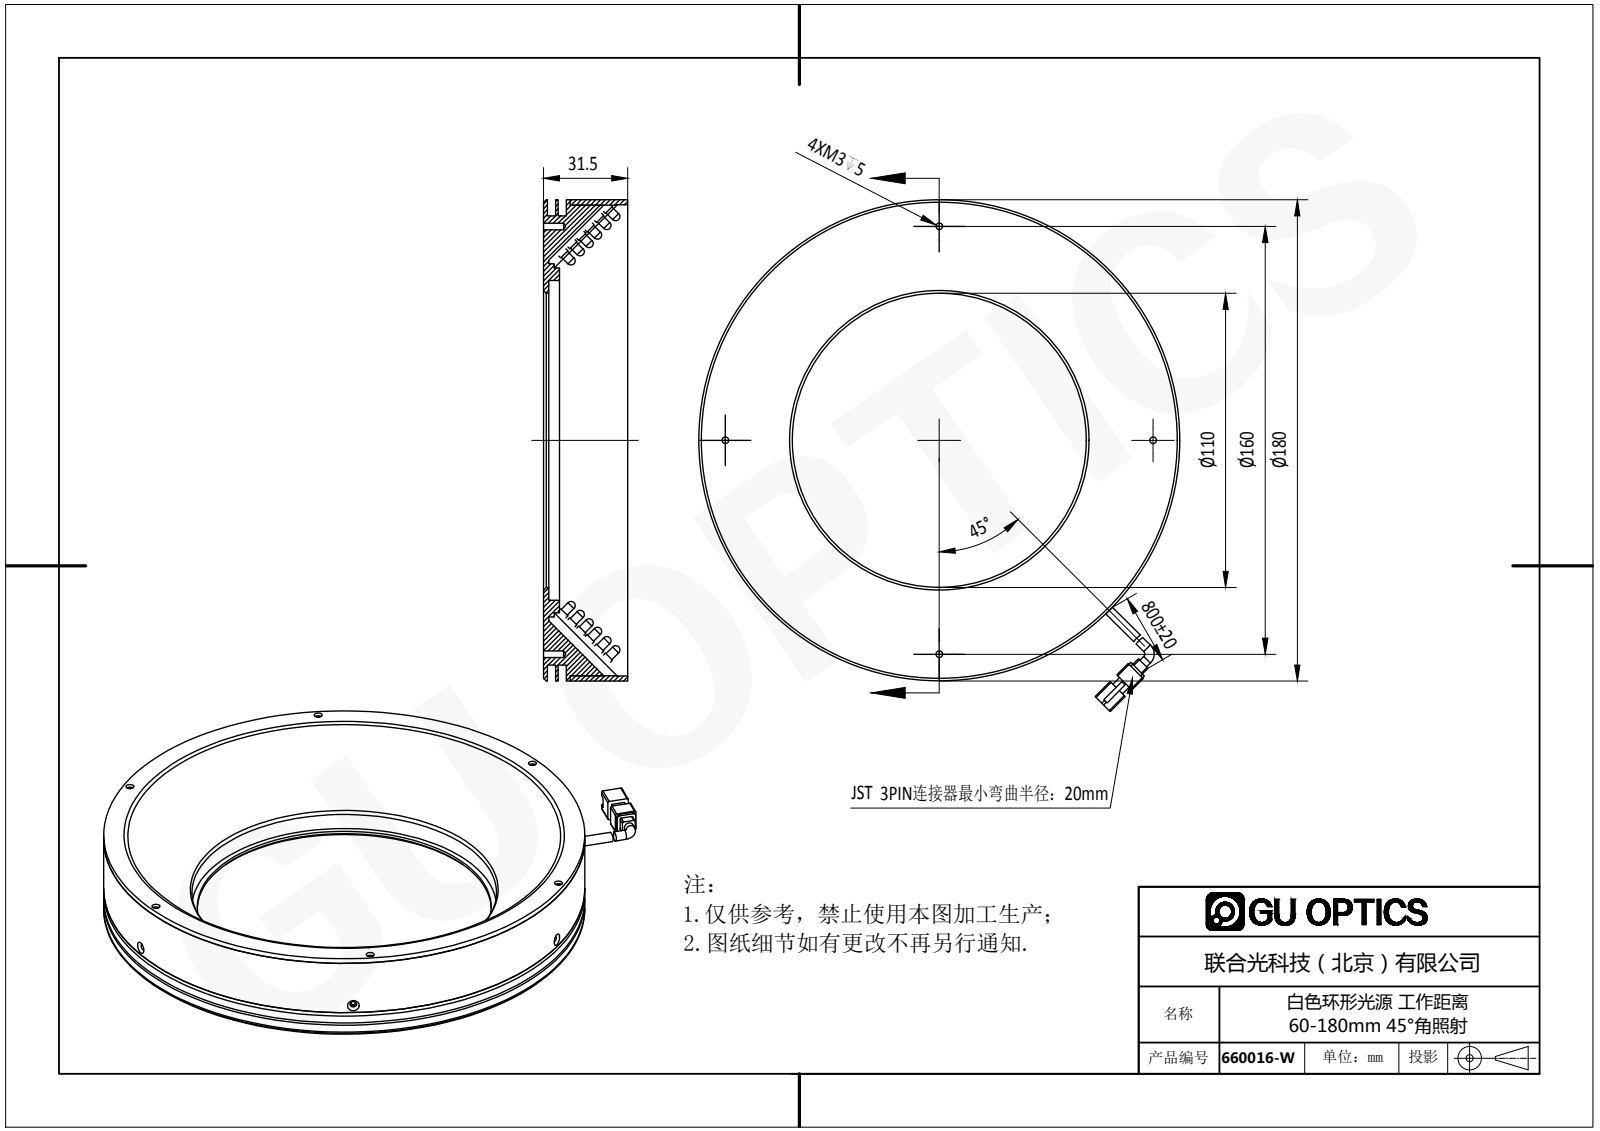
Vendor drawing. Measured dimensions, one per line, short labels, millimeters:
name: 660016-W
written by: SolidWorks 2016 (AUTOMOTIVE_DESIGN)
unit: mm
bodies: 546 solids, 9482 faces (6561 planar, 2312 cylindrical, 609 other)
size: 191.47 × 180 × 33.5
volume: 236 719 mm³; area: 217 058 mm²
holes: 7× ⌀3.5, 6× ⌀1.25, 6× ⌀1.5, 6× ⌀3, 4× ⌀1.6, 4× ⌀2.5, 3× ⌀2.4, 1× ⌀110, 1× ⌀114, 1× ⌀119.6, 1× ⌀172.4
bosses: 540× ⌀3.8, 540× ⌀3, 2× ⌀3.5, 1× ⌀180, 1× ⌀176, 1× ⌀168, 1× ⌀132, 1× ⌀129
rounds: 8× R0.5, 4× R1, 1× R7.5
face distances: 4, 31.5, 2, 0.5, 1.5, 4.5, 3, 2.5, 5.5, 8.5
hole spacings: 87.5, 151.56, 39.06, 51.47, 128.2, 151.55, 167.26, 170.58
